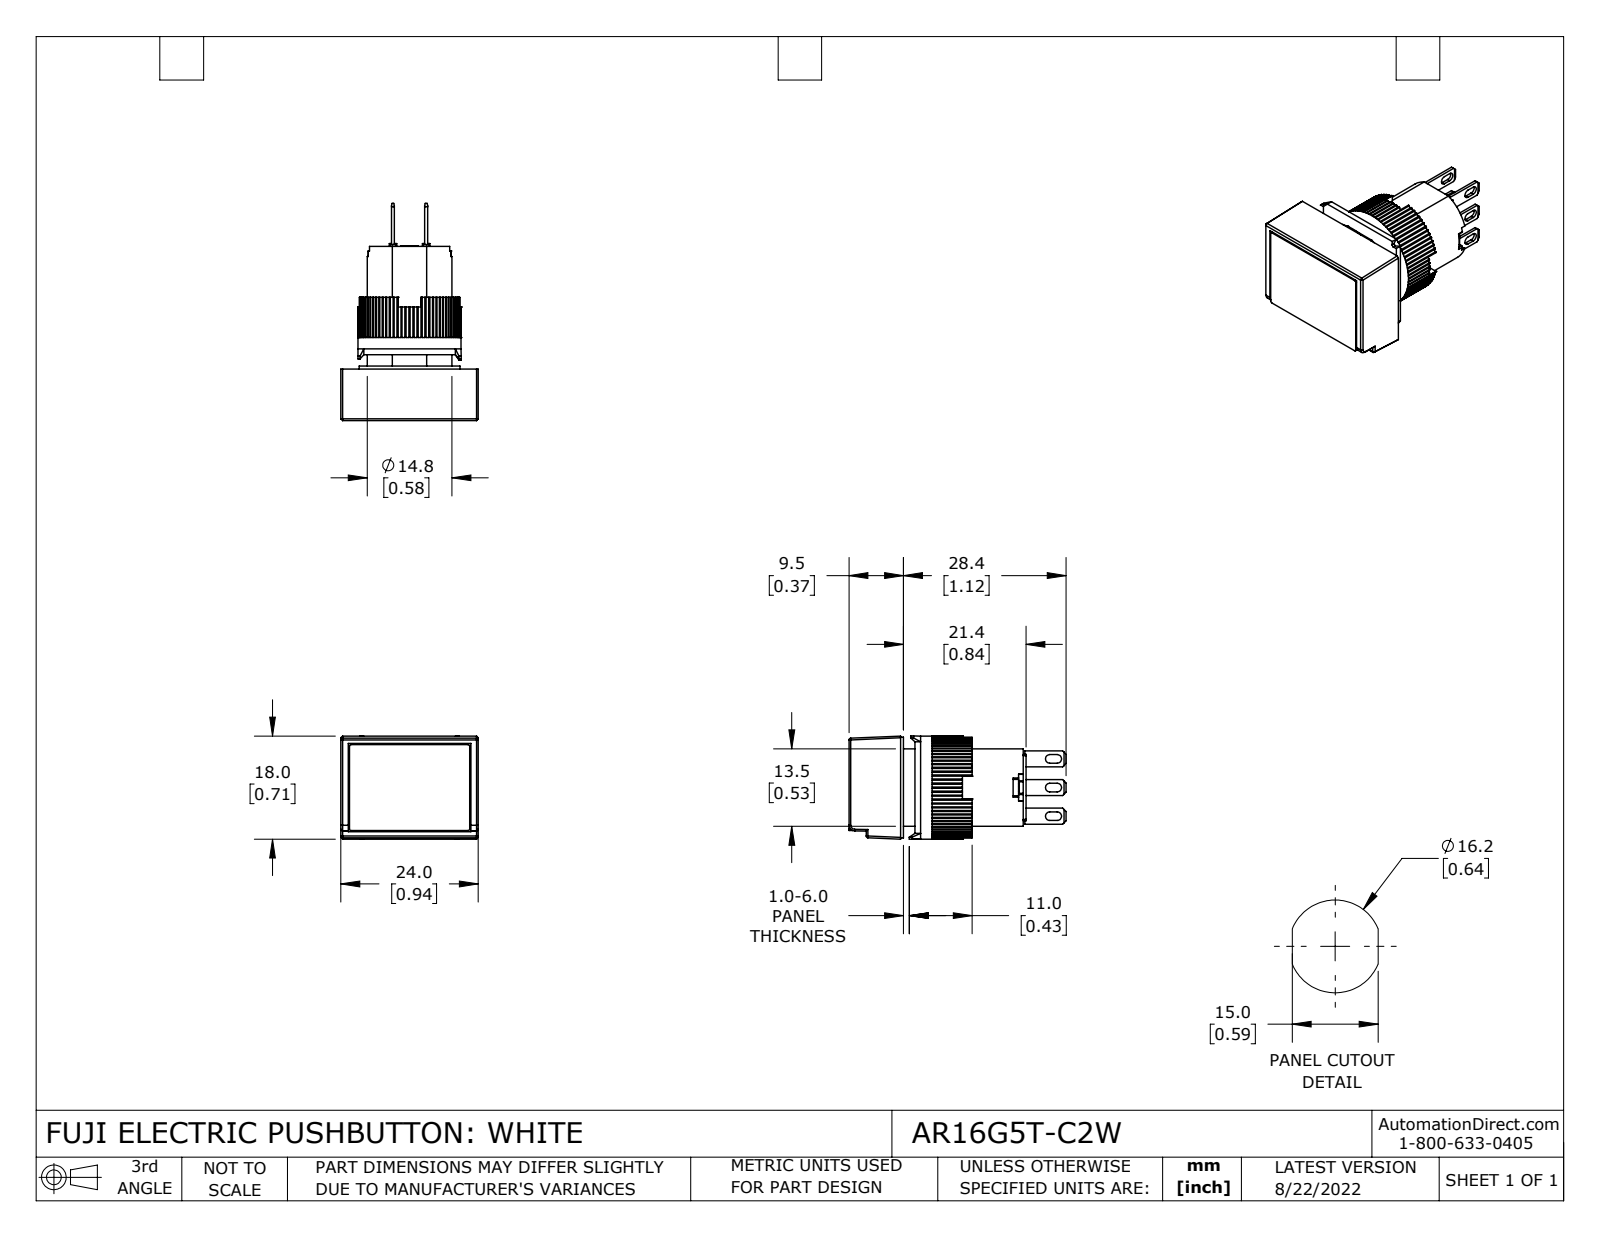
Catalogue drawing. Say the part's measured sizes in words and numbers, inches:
The part is named "AR16G5T-C2W". Its 3-D file was written by "SolidWorks 2021 (CONFIG_CONTROL_DESIGN)". It is 12 solids with 811 faces: 630 planar, 175 cylindrical and 6 other. Overall it measures 1.492 by 0.945 by 0.709 inches. Its volume is 0.447 cubic inches and its surface area 9.321 square inches. Round holes: 1 of diameter 0.543, 1 of diameter 0.583. Round bosses or shafts: 1 of diameter 0.709, 1 of diameter 0.693. Partial cylindrical surfaces (rounded edges, fillets, slot ends): 80 of radius 0.01, 12 of radius 0.008, 6 of radius 0.012, 6 of radius 0.03, 1 of radius 0.039. The main face-to-face distances are 0.213, 0.354, 0.142, 0.492, 0.35, 0.138, 0.02, 0.843, 0.059, 0.453.
